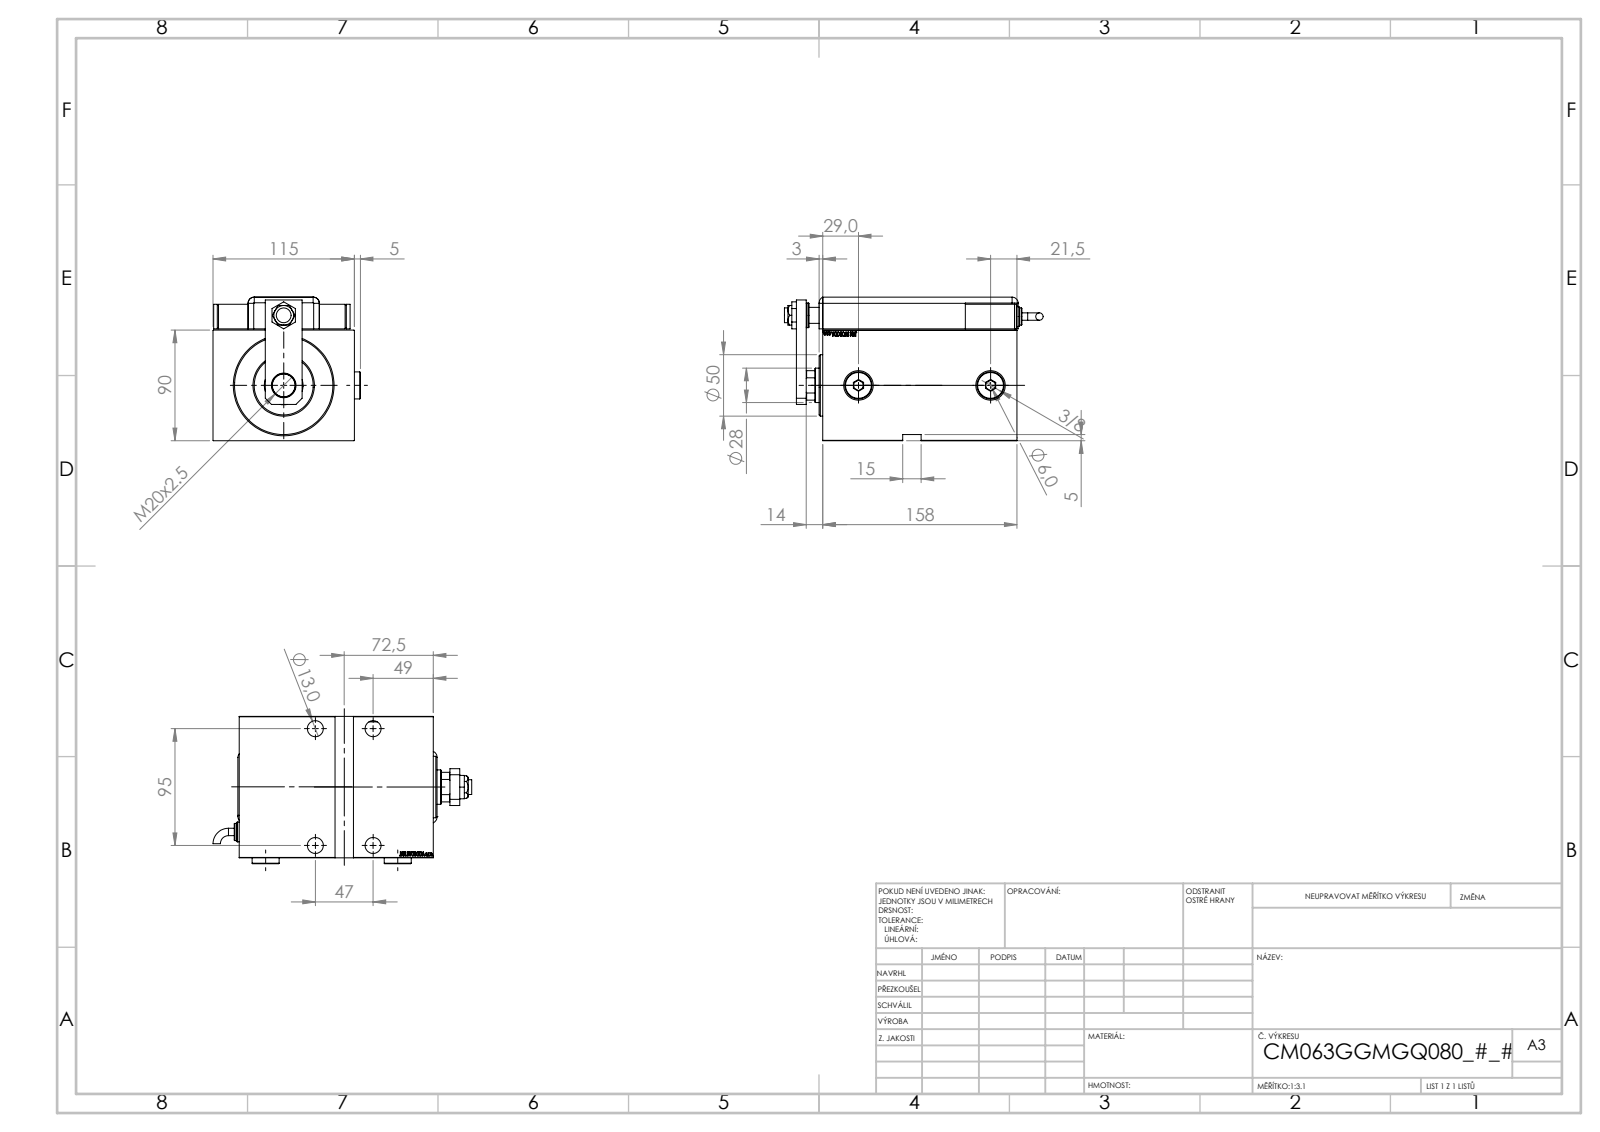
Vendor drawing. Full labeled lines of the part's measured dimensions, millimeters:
Part name (STEP PRODUCT): ZARAZKA_Q; MAGNETIC SWITCH Q; NUT_D13; Zatka_OIL_PORT (+7 more)
STEP written by: SolidWorks 2019 (CONFIG_CONTROL_DESIGN)
Units: millimetres
Bodies: 15 solids, 1280 faces (648 planar, 111 cylindrical, 521 other)
Overall size (bounding box): 210.46 × 119.9 × 116.8
Volume: 1 515 000 mm³ · Surface area: 241 225 mm²
Round holes (diameter × count): ⌀13 ×5, ⌀19 ×4, ⌀4 ×2, ⌀6 ×2, ⌀8 ×2, ⌀16.17 ×2, ⌀24 ×2, ⌀12 ×1, ⌀14 ×1, ⌀18.5 ×1, ⌀20 ×1, ⌀28 ×1
Round bosses / shafts (diameter × count): ⌀20 ×3, ⌀22 ×2, ⌀16 ×2, ⌀14 ×2, ⌀6 ×2, ⌀50 ×1
Partial cylindrical surfaces — rounded edges, fillets, slot ends (radius × count): R5 ×9, R10 ×1, R13.5 ×1
Main face-to-face distances: 90, 115, 3, 158, 5, 116.8, 26.8, 1, 17.5, 28.5
Hole centre spacings: 47, 55.93, 70.91, 95, 96.12, 105.54, 105.99, 20
